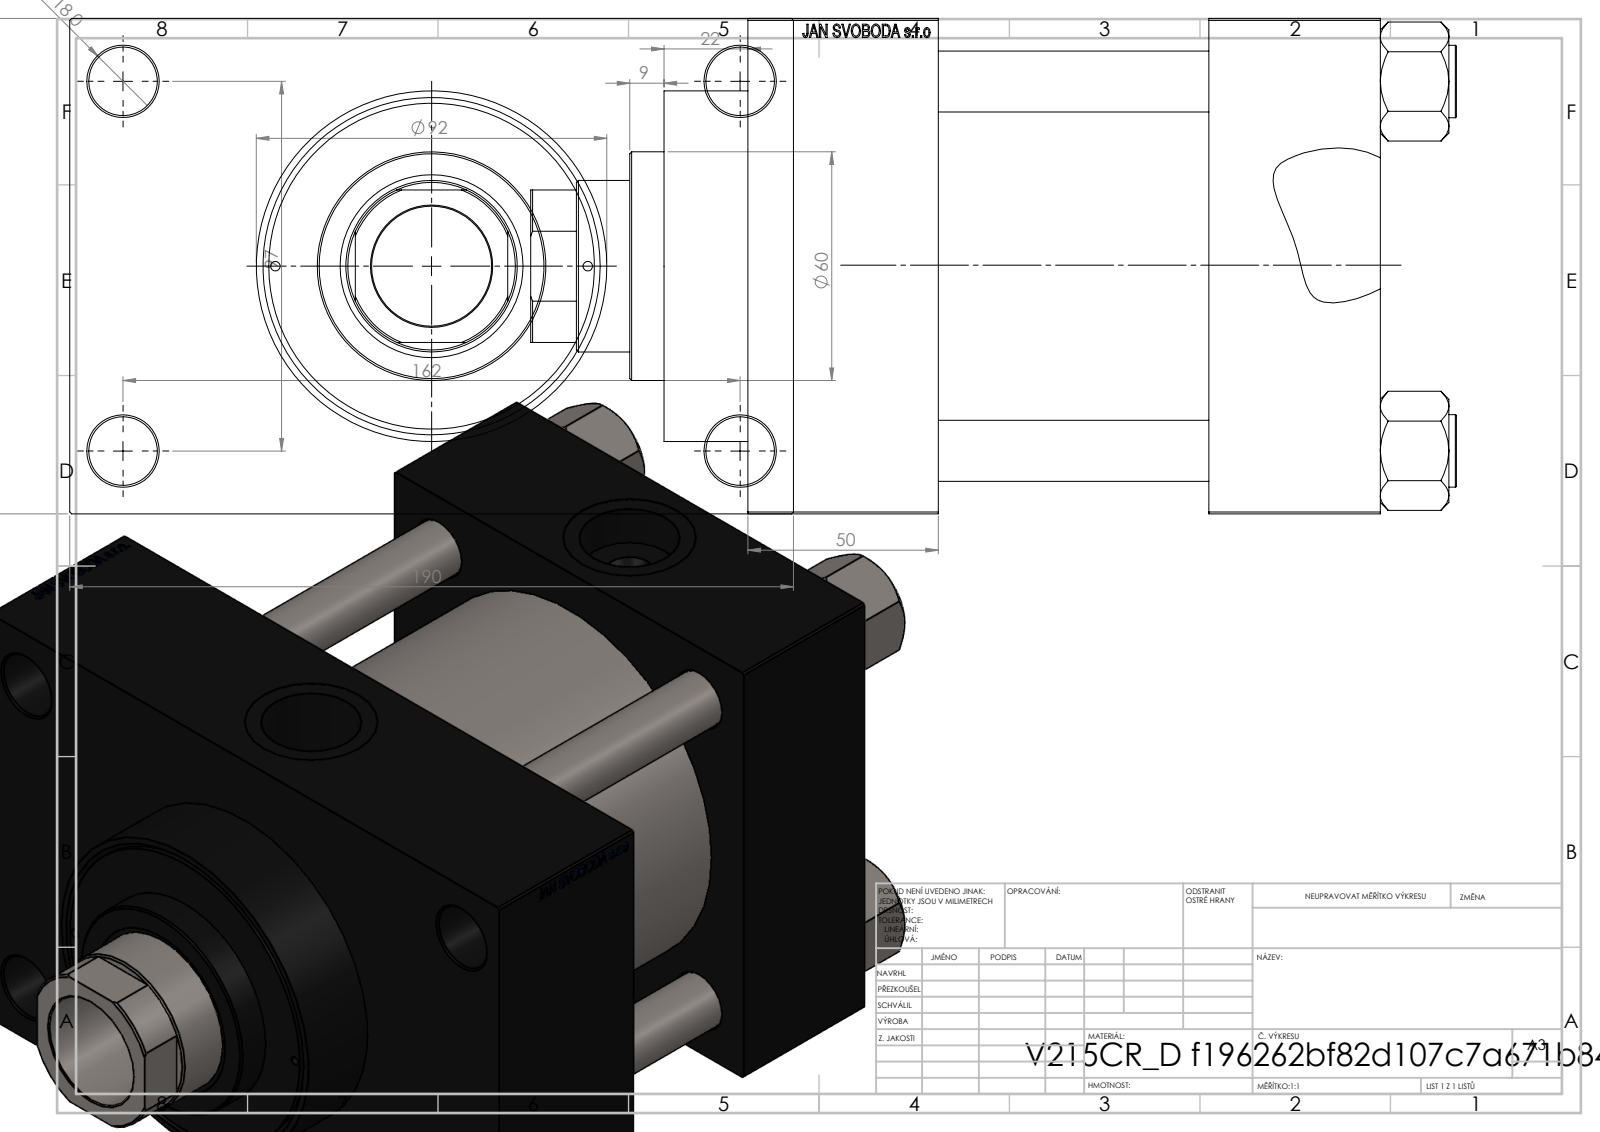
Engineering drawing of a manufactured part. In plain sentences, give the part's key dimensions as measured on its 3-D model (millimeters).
The part is named "V215_VC_A; V215CR_D_Body; V215CR_D_TYCINKA; NUT_M5_D (+1 more)". Its 3-D file was written by "SolidWorks 2019 (CONFIG_CONTROL_DESIGN)". It is 11 solids with 1160 faces: 547 planar, 93 cylindrical and 520 other. Overall it measures 243 by 190 by 130 millimeters. Its volume is 2 606 000 cubic millimeters and its surface area 352 239 square millimeters. Round holes: 4 of diameter 16, 4 of diameter 18, 2 of diameter 2.5, 2 of diameter 7, 2 of diameter 26.44, 2 of diameter 35, 1 of diameter 31.5, 1 of diameter 45, 1 of diameter 48, 1 of diameter 76, 1 of diameter 85.5, 1 of diameter 100. Round bosses or shafts: 4 of diameter 19, 1 of diameter 106, 1 of diameter 92, 1 of diameter 60. Partial cylindrical surfaces (rounded edges, fillets, slot ends): 1 of radius 22. The main face-to-face distances are 130, 45, 116, 71, 166, 121, 50, 30, 160, 20. The hole center spacings are 32.55, 49.02, 62.87, 68.52, 94.41, 96.9, 101.73, 102.27.
